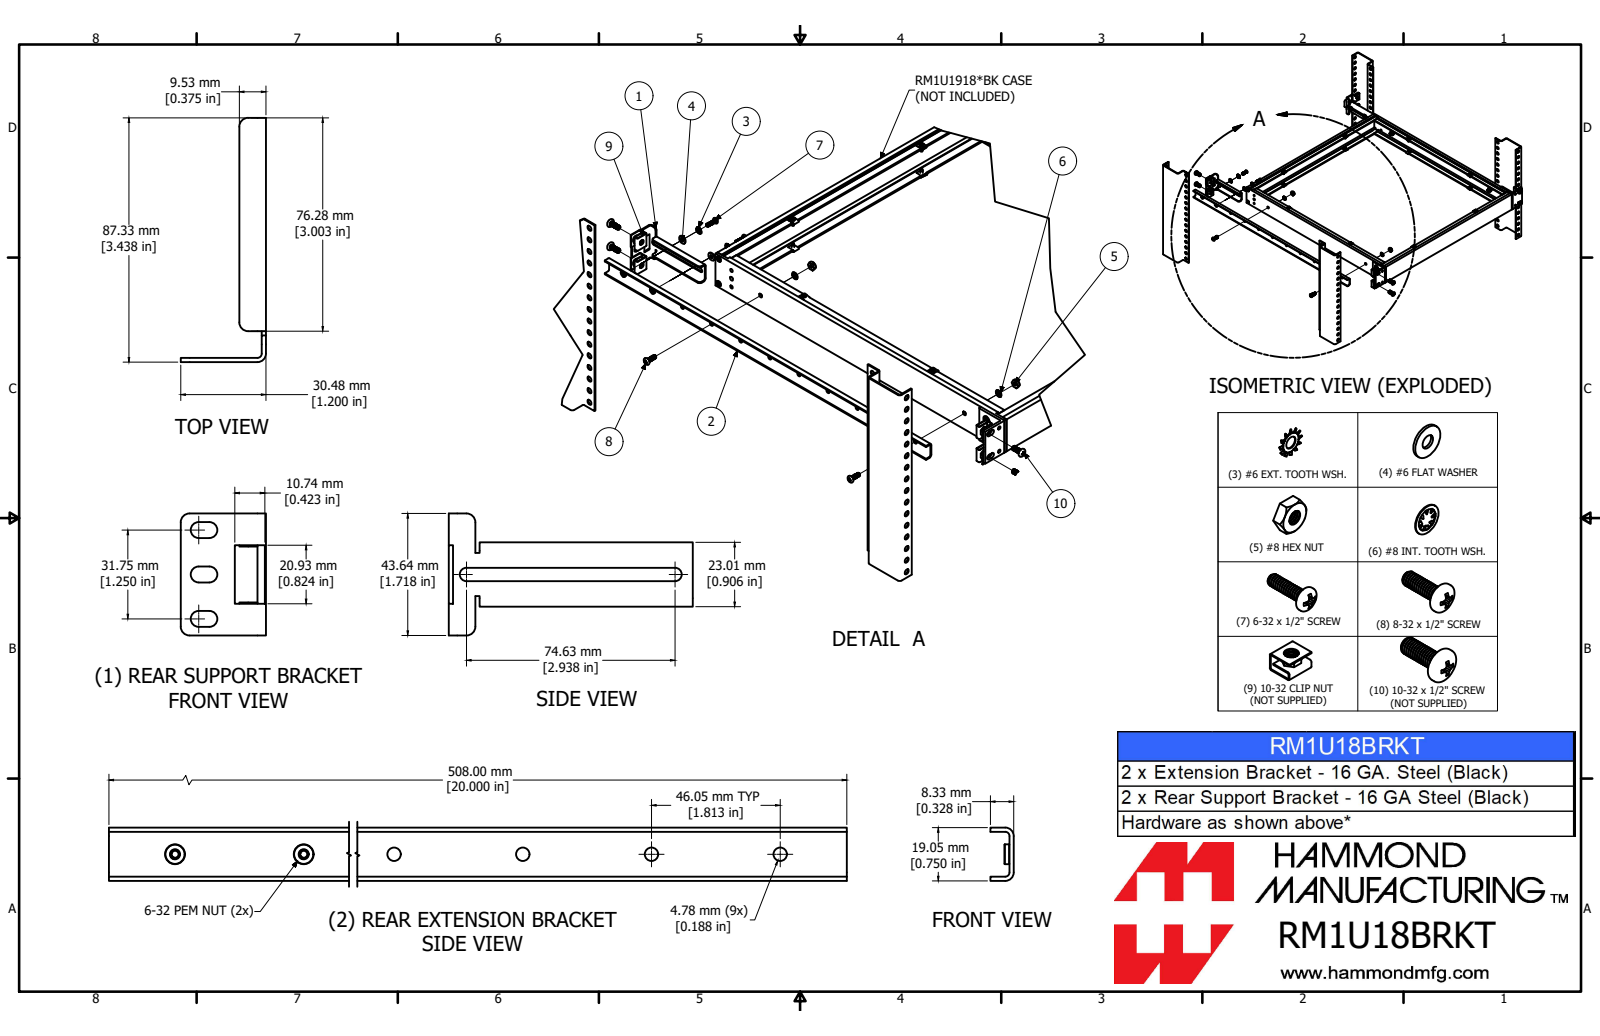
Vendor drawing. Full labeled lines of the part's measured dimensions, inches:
Part name (STEP PRODUCT): RM1U18BRKT
STEP written by: SolidWorks 2021 (AUTOMOTIVE_DESIGN)
Units: inches
Bodies: 4 solids, 397 faces (266 planar, 115 cylindrical, 16 other)
Overall size (bounding box): 20.349 × 1.718 × 1.2
Volume: 1.785 in³ · Surface area: 64.47 in²
Round holes (diameter × count): ⌀0.188 ×11, ⌀0.097 ×2, ⌀0.138 ×2
Round bosses / shafts (diameter × count): ⌀0.28 ×2
Partial cylindrical surfaces — rounded edges, fillets, slot ends (radius × count): R0.125 ×6, R0.06 ×5, R0.12 ×5, R0.113 ×4, R0.094 ×2, R0.106 ×2, R0.112 ×2
Main face-to-face distances: 0.06, 0.691, 0.75, 0.631, 0.078, 0.769, 0.328, 0.268, 0.12, 0.388
Hole centre spacings: 1.813, 3.626, 5.439, 7.252, 9.065, 10.878, 12.691, 14.504
